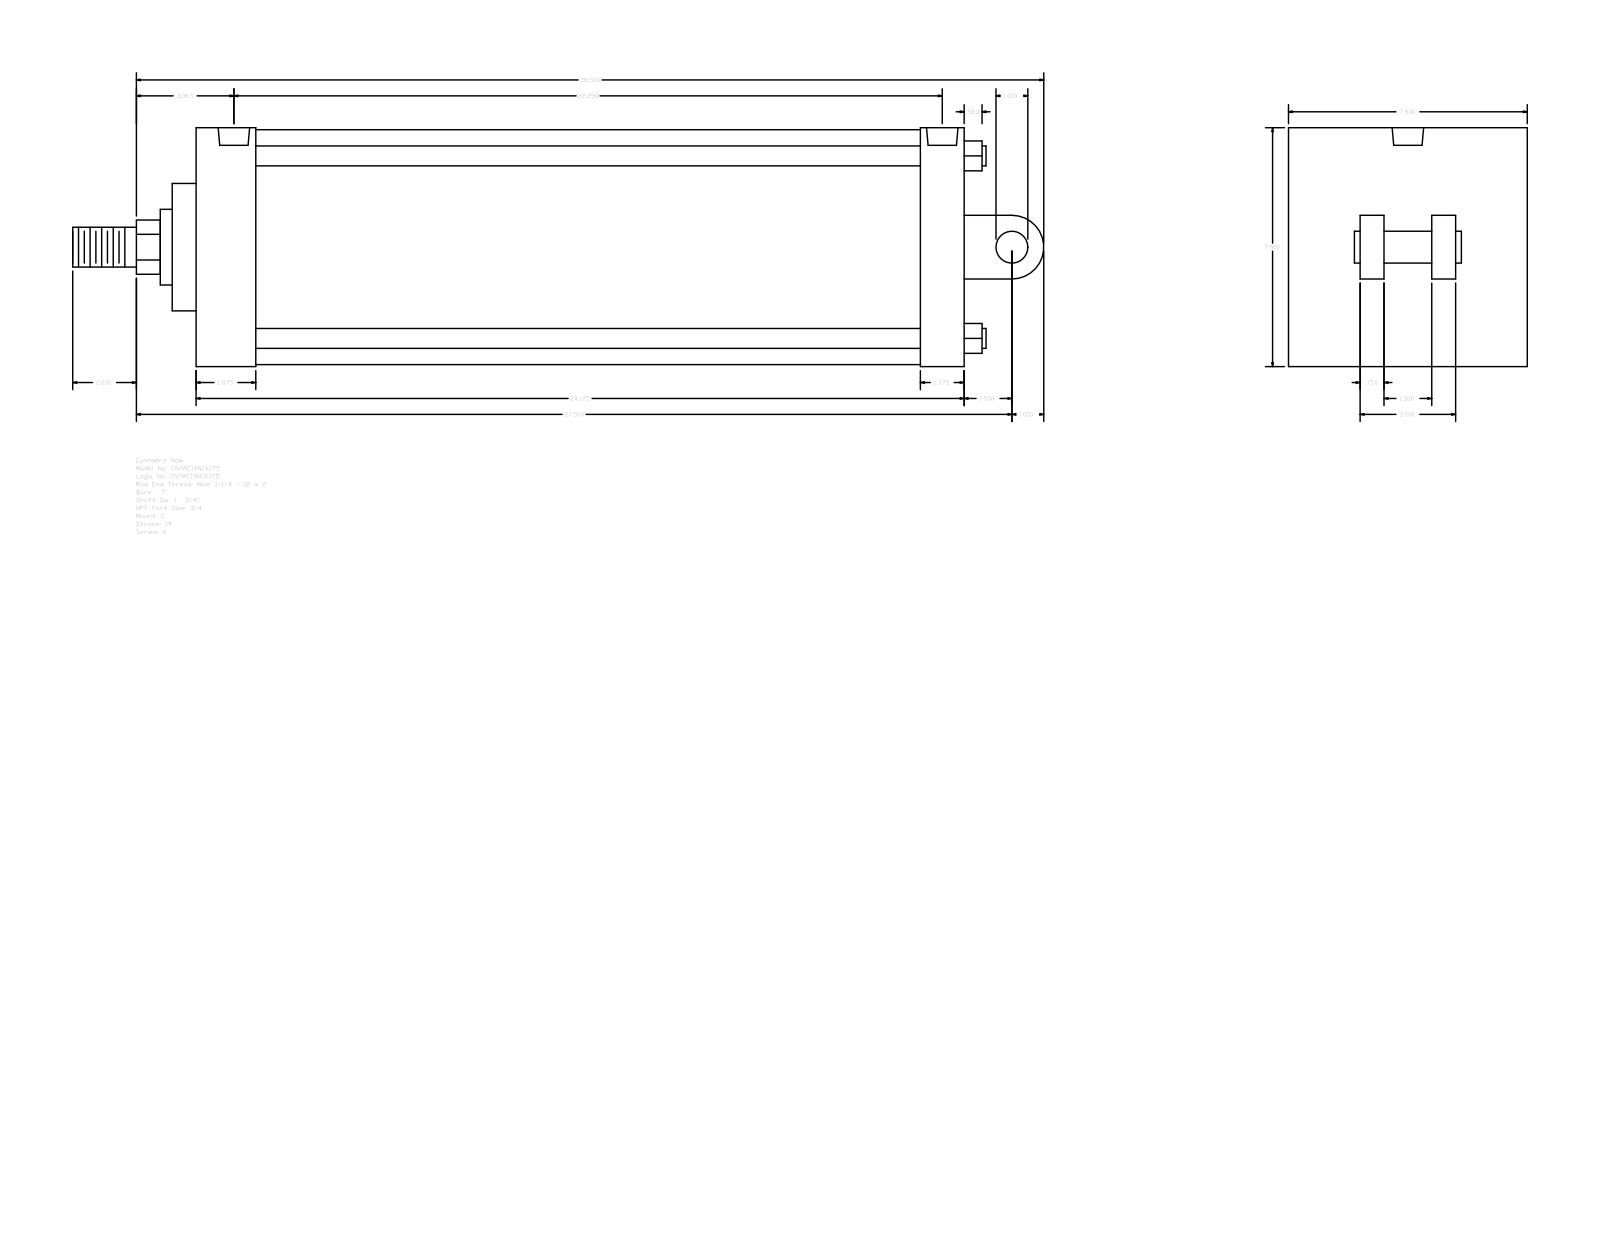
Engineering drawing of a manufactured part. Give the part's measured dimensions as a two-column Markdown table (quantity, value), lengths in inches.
| quantity | value |
| --- | --- |
| part name | A_C__0700_1.75 |
| STEP written by | GSSL Pune (CONFIG_CONTROL_DESIGN) |
| units | inches |
| bodies | 0 solids, 104 faces (75 planar, 29 cylindrical, 0 other) |
| overall size | 30.5 × 7.5 × 7.5 |
| round holes (diameter × count) | 0.594 × 4, 0.989 × 2 |
| round bosses / shafts (diameter × count) | 0.625 × 4, 7.375 × 1, 2.375 × 1, 1.75 × 1, 1.25 × 1, 1 × 1 |
| partial cylindrical surfaces (radius × count) | 0.852 × 1, 1 × 1 |
| main face-to-face distances | 7.5, 24.125, 0.75, 3, 2.25, 5.75, 1.75, 2.75, 1.875, 22.25 |
| hole center spacings | 0.219, 21.812, 22.031, 22.25 |
